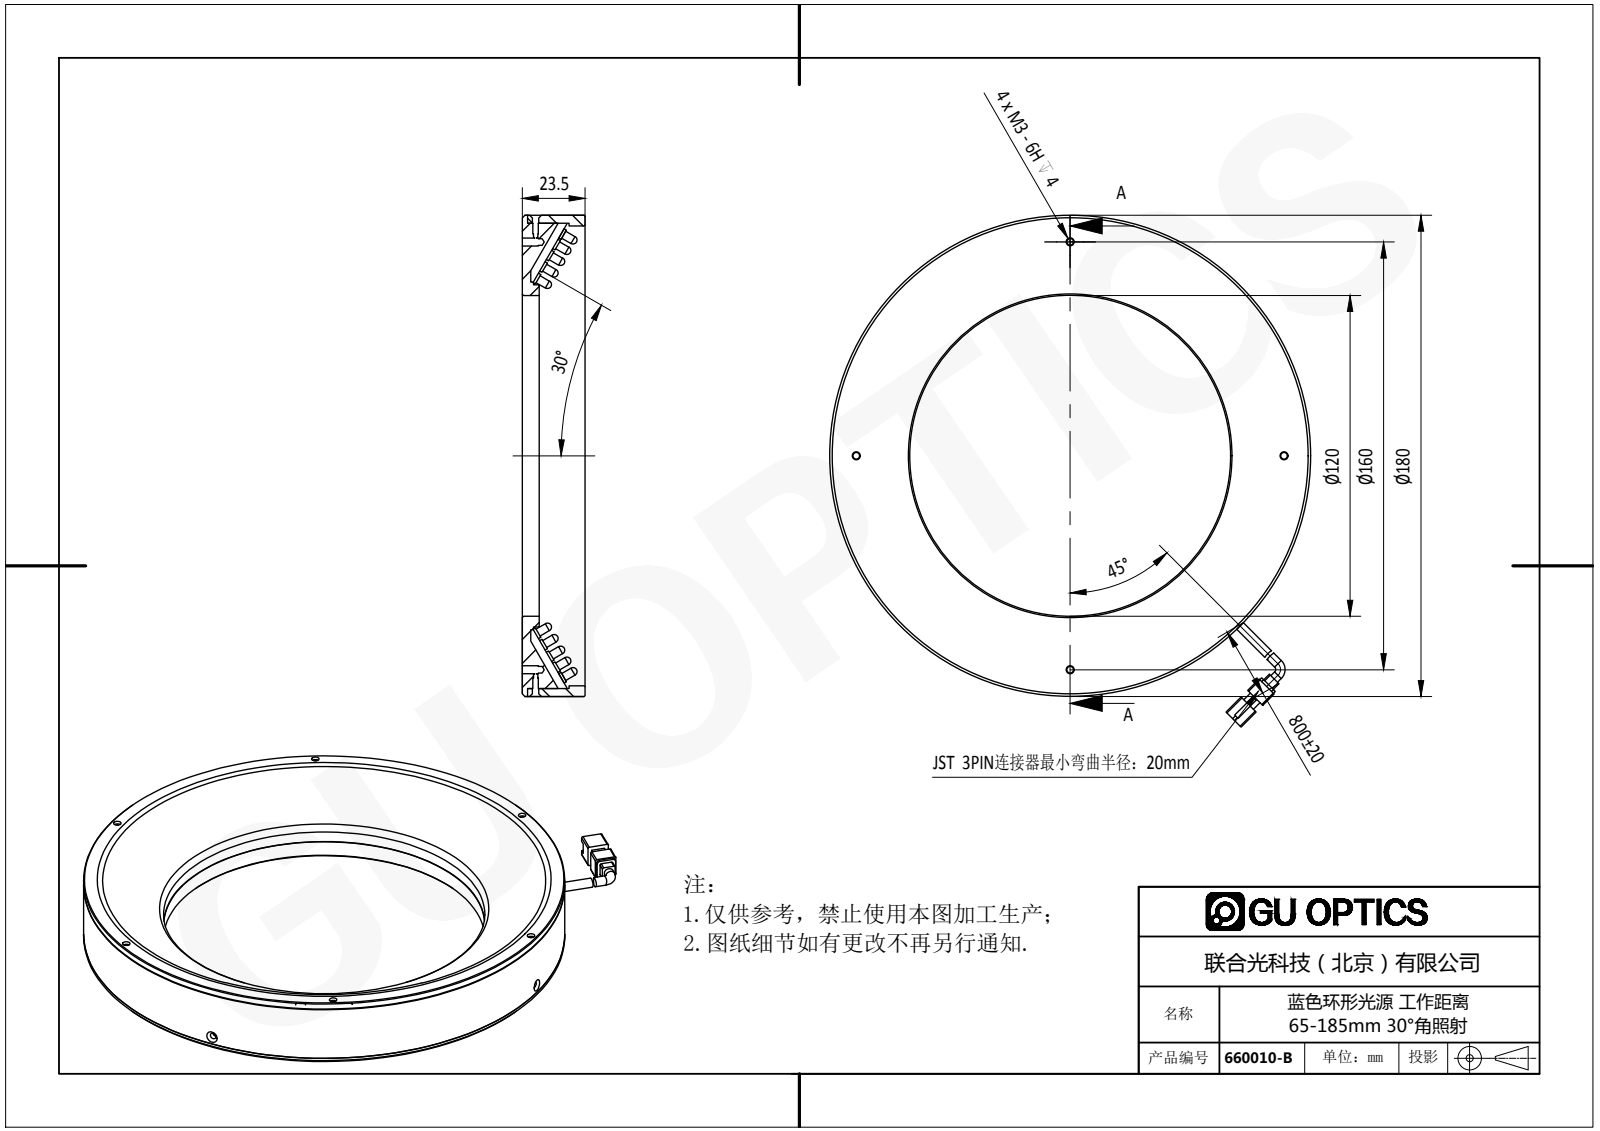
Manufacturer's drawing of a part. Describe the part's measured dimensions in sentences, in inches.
The part is named "660010-B". Its 3-D file was written by "SolidWorks 2016 (AUTOMOTIVE_DESIGN)". It is 326 solids with 5763 faces: 3930 planar, 1439 cylindrical and 394 other. Overall it measures 7.538 by 7.087 by 1.024 inches. Its volume is 11.86 cubic inches and its surface area 246.8 square inches. Round holes: 8 of diameter 0.063, 6 of diameter 0.049, 6 of diameter 0.059, 6 of diameter 0.11, 4 of diameter 0.098, 4 of diameter 0.118, 4 of diameter 0.138, 2 of diameter 0.079, 2 of diameter 0.094, 1 of diameter 0.142, 1 of diameter 4.724, 1 of diameter 4.732. Round bosses or shafts: 320 of diameter 0.15, 320 of diameter 0.118, 2 of diameter 0.138, 1 of diameter 7.087, 1 of diameter 6.85, 1 of diameter 5.118, 1 of diameter 5.039, 1 of diameter 4.929. Partial cylindrical surfaces (rounded edges, fillets, slot ends): 8 of radius 0.02, 4 of radius 0.039, 1 of radius 0.354. The main face-to-face distances are 0.925, 0.079, 0.846, 0.098, 1.024, 0.945, 0.039, 0.048, 0.127, 0.798. The hole center spacings are 3.445, 5.967, 1.73, 3.15, 3.307, 4.454, 4.668, 5.713.
